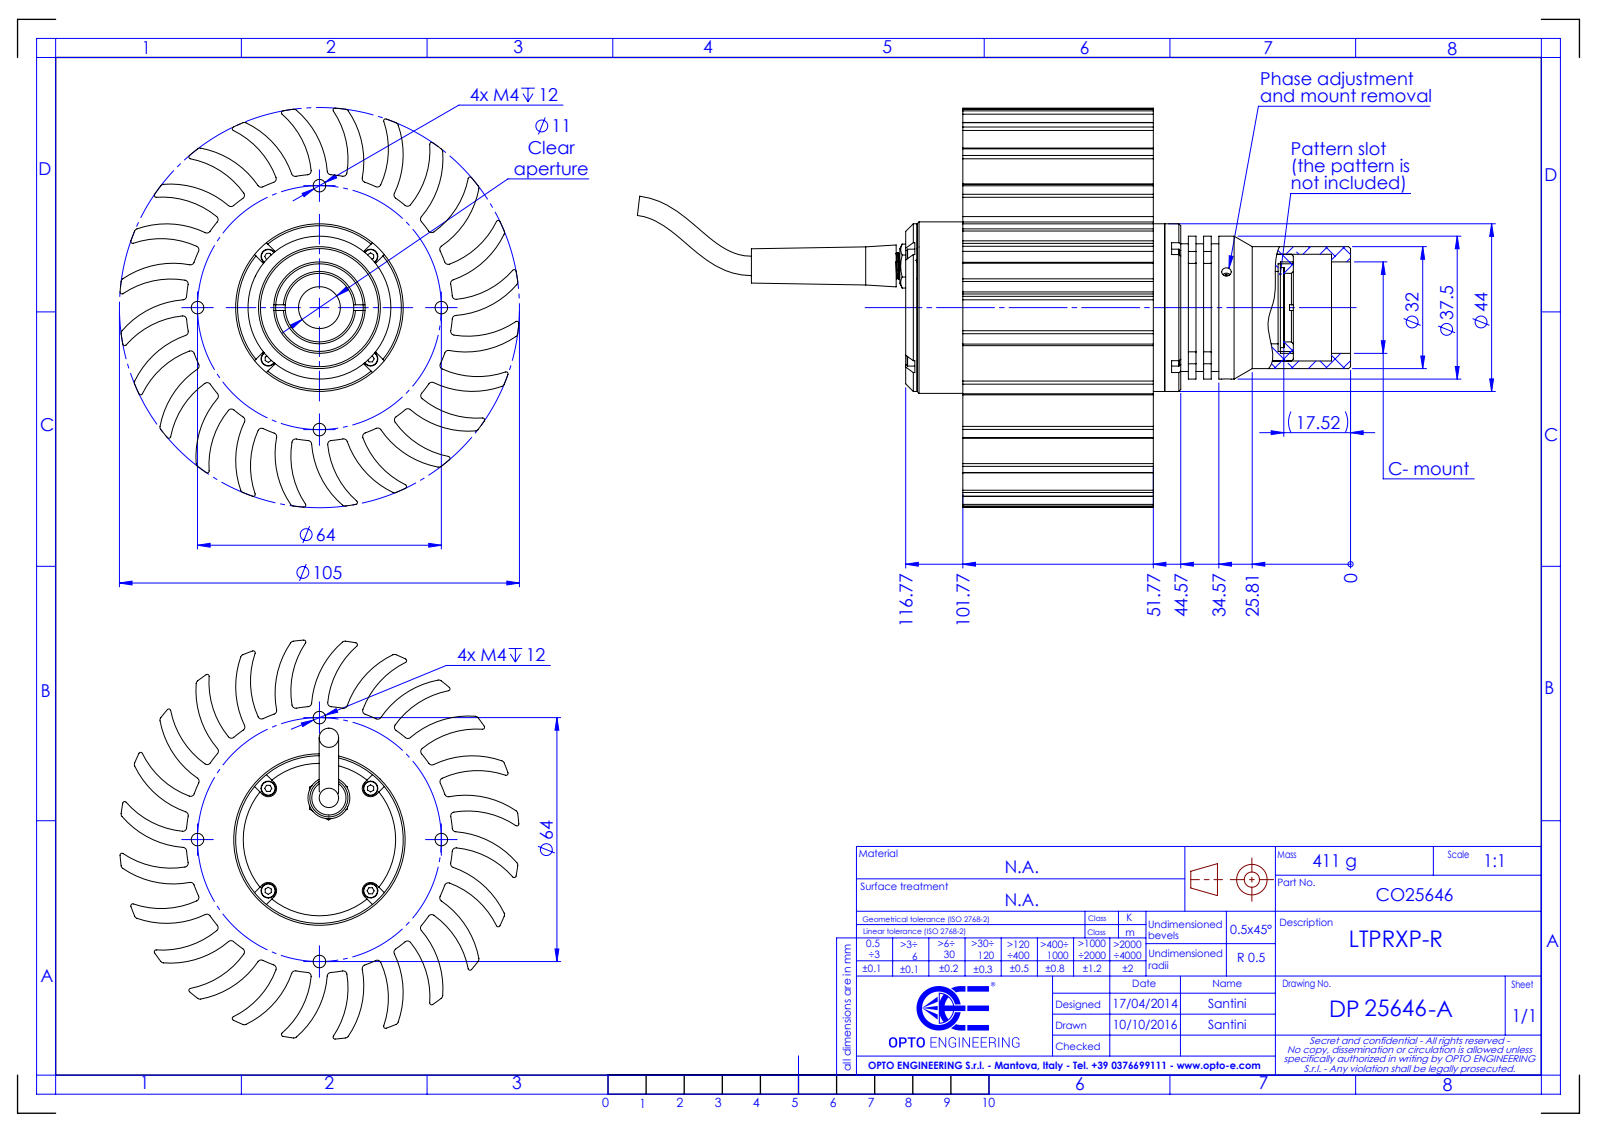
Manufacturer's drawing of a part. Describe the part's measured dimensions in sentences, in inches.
The part is named "DP25646-A_LTPRXP-R". Its 3-D file was written by "SolidWorks 2021 (CONFIG_CONTROL_DESIGN)". It is 0 solids with 476 faces: 102 planar, 314 cylindrical and 60 other. Overall it measures 7.37 by 4.121 by 4.121 inches. Round holes: 4 of diameter 0.13, 3 of diameter 0.098, 1 of diameter 0.945, 1 of diameter 1.102. Round bosses or shafts: 4 of diameter 0.15, 1 of diameter 1.772, 1 of diameter 1.732, 1 of diameter 1.476, 1 of diameter 1.319, 1 of diameter 1.26. Partial cylindrical surfaces (rounded edges, fillets, slot ends): 72 of radius 0.039, 24 of radius 0.02, 24 of radius 0.889, 24 of radius 0.925, 4 of radius 0.087, 4 of radius 0.089, 1 of radius 1.378, 1 of radius 2.067. The main face-to-face distances are 1.969, 2.559, 0.118, 0.591, 2.677, 2.087, 0.079, 0.472, 2.441, 0.157. The hole center spacings are 1.26, 1.781, 2.52.
